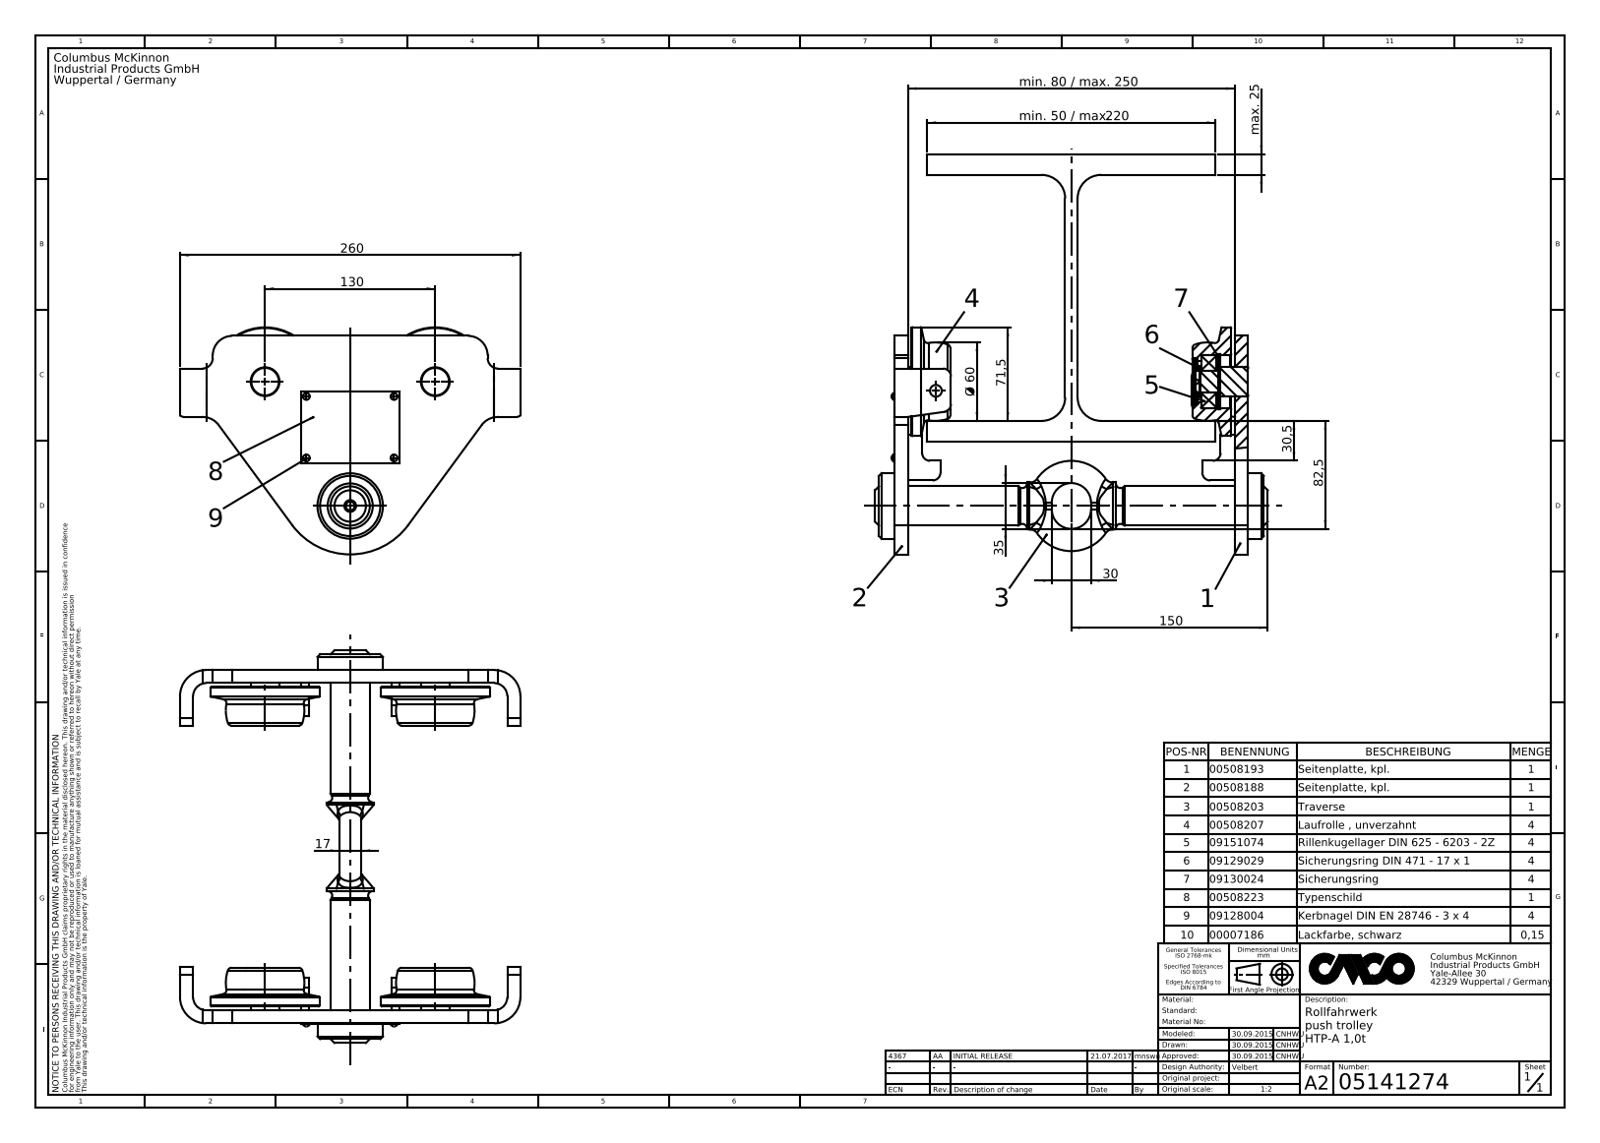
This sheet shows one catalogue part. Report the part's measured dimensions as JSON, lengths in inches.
{"part_name": "HTP-A 1,0t", "step_written_by": "SolidWorks 2015 (AUTOMOTIVE_DESIGN)", "units": "inches", "bodies": {"solids": 35, "faces": 824, "planar": 240, "cylindrical": 344, "other": 240}, "overall_size": [19.685, 12.047, 11.811], "volume_in3": 351.5, "surface_area_in2": 1496, "round_holes": [[0.067, 8], [0.098, 8], [0.118, 4], [0.138, 4], [0.079, 2], [0.354, 2], [0.638, 2], [0.866, 2], [1.217, 2], [1.26, 2], [1.339, 2], [1.406, 2]], "round_bosses_or_shafts": [[0.205, 4], [3.268, 2], [1.673, 2], [0.937, 2], [0.669, 2], [0.63, 2], [1.969, 1], [1.575, 1]], "partial_cylinders_radius": [[0.067, 8], [0.098, 8], [0.236, 8], [0.394, 4], [0.591, 4], [0.709, 4], [0.787, 4], [0.315, 2]], "face_to_face_distances": [0.63, 8.031, 8.661, 7.402, 0.374, 5.128, 5.502, 0.394, 10.236, 4.734], "hole_center_spacings": [5.118, 0.33, 0.393, 0.722, 0.387, 0.167, 0.246, 0.556]}
